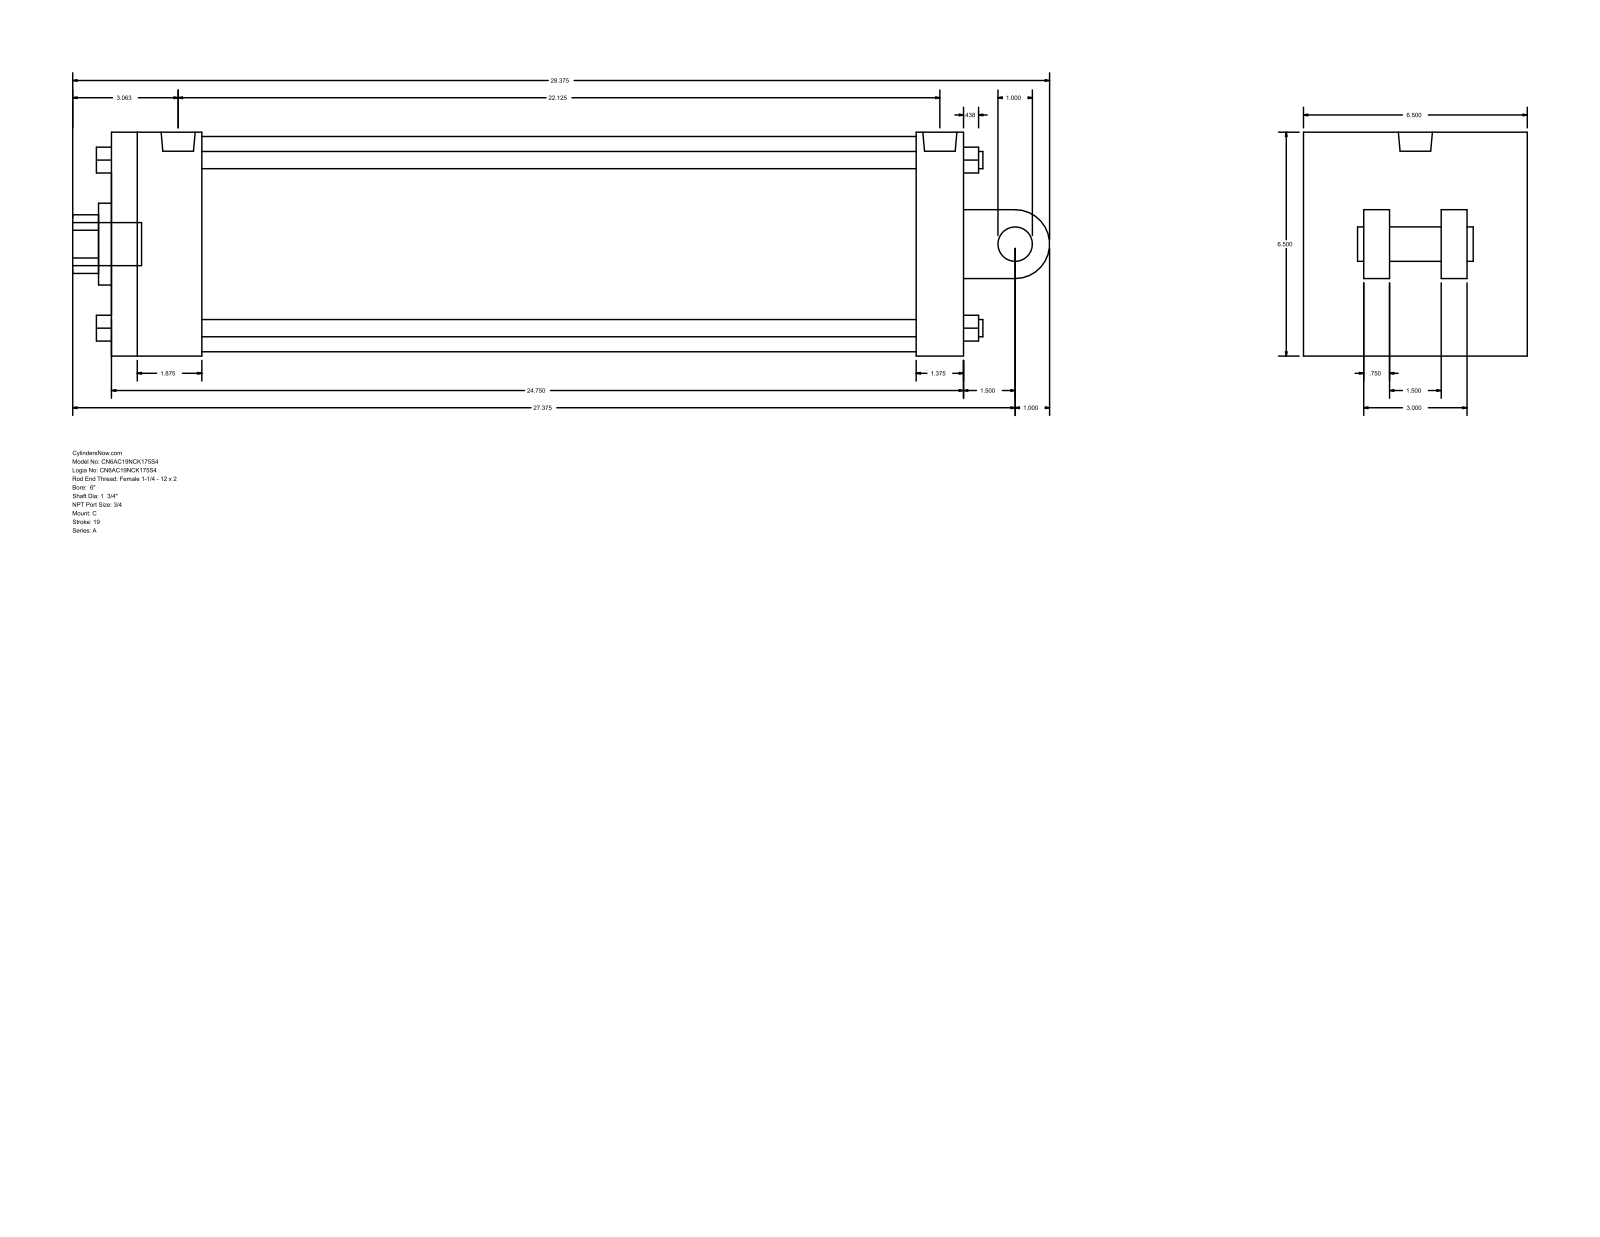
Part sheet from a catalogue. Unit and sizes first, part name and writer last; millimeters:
Units: millimetres
Overall size (bounding box): 720.73 × 165.1 × 165.1
Round holes (diameter × count): ⌀15.08 ×2, ⌀25.12 ×1, ⌀44.45 ×1, ⌀60.33 ×1, ⌀158.75 ×1
Round bosses / shafts (diameter × count): ⌀12.7 ×4, ⌀15.08 ×2, ⌀31.75 ×1, ⌀25.4 ×1, ⌀25.12 ×1
Partial cylindrical surfaces — rounded edges, fillets, slot ends (radius × count): R21.63 ×1, R25.4 ×1
Main face-to-face distances: 165.1, 628.66, 19.05, 57.15, 66.68, 561.98, 593.73, 527.05, 34.93, 44.45
Hole centre spacings: 5.56
Bodies: 0 solids, 135 faces (102 planar, 33 cylindrical, 0 other)
Part name (STEP PRODUCT): A_C__0600_1.75
STEP written by: GSSL Pune (CONFIG_CONTROL_DESIGN)
